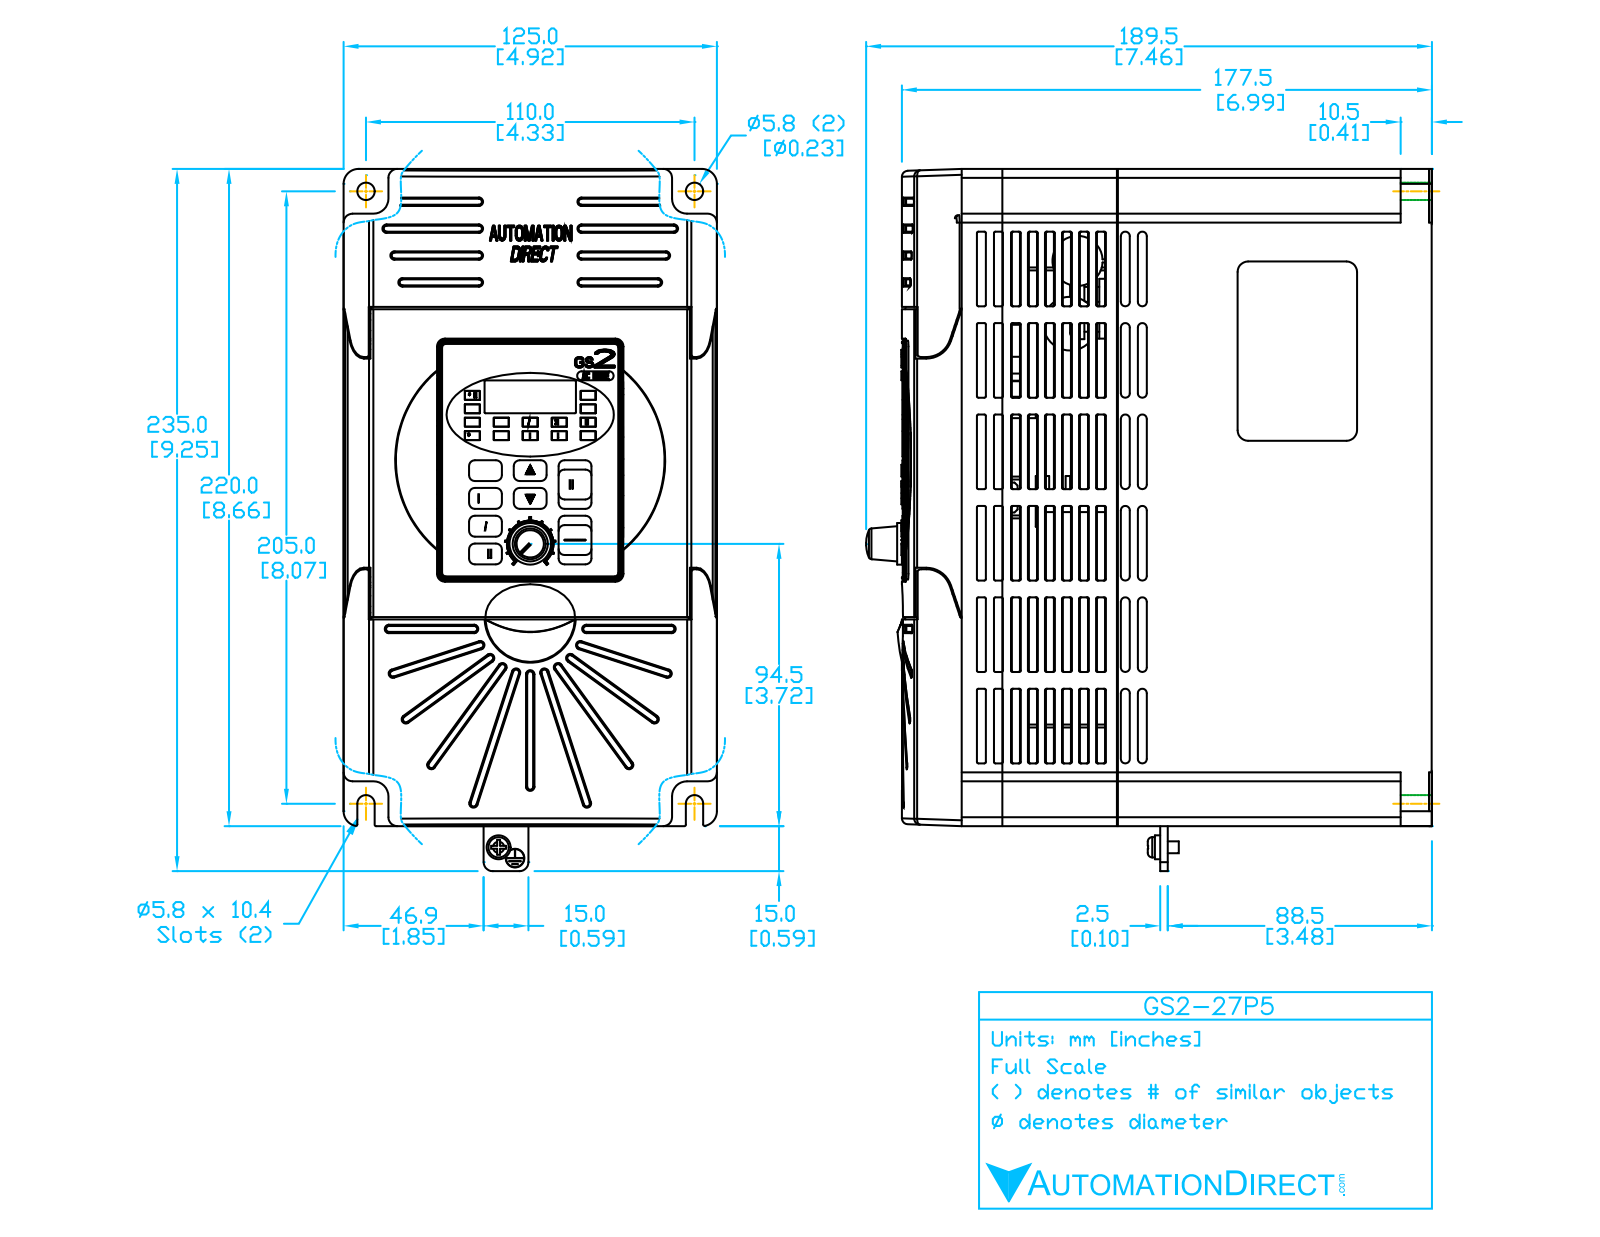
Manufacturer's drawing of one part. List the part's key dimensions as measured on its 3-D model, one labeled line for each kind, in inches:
Part name (STEP PRODUCT): GS2-27P5
STEP written by: SolidWorks 2013 (AUTOMOTIVE_DESIGN)
Units: inches
Bodies: 1 solid, 790 faces (352 planar, 218 cylindrical, 220 other)
Overall size (bounding box): 9.25 × 7.485 × 4.92
Volume: 282.9 in³ · Surface area: 350.8 in²
Round holes (diameter × count): ⌀0.23 ×2, ⌀3.2 ×1
Round bosses / shafts (diameter × count): ⌀0.545 ×1, ⌀0.258 ×1, ⌀0.15 ×1
Partial cylindrical surfaces — rounded edges, fillets, slot ends (radius × count): R0.06 ×40, R0.04 ×38, R0.125 ×12, R0.2 ×8, R0.019 ×6, R0.064 ×6, R0.25 ×6, R0.1 ×4
Main face-to-face distances: 0.015, 4.905, 4.92, 6.181, 8.645, 4.89, 8.66, 6.17, 0.58, 0.565
Hole centre spacings: 4.33
